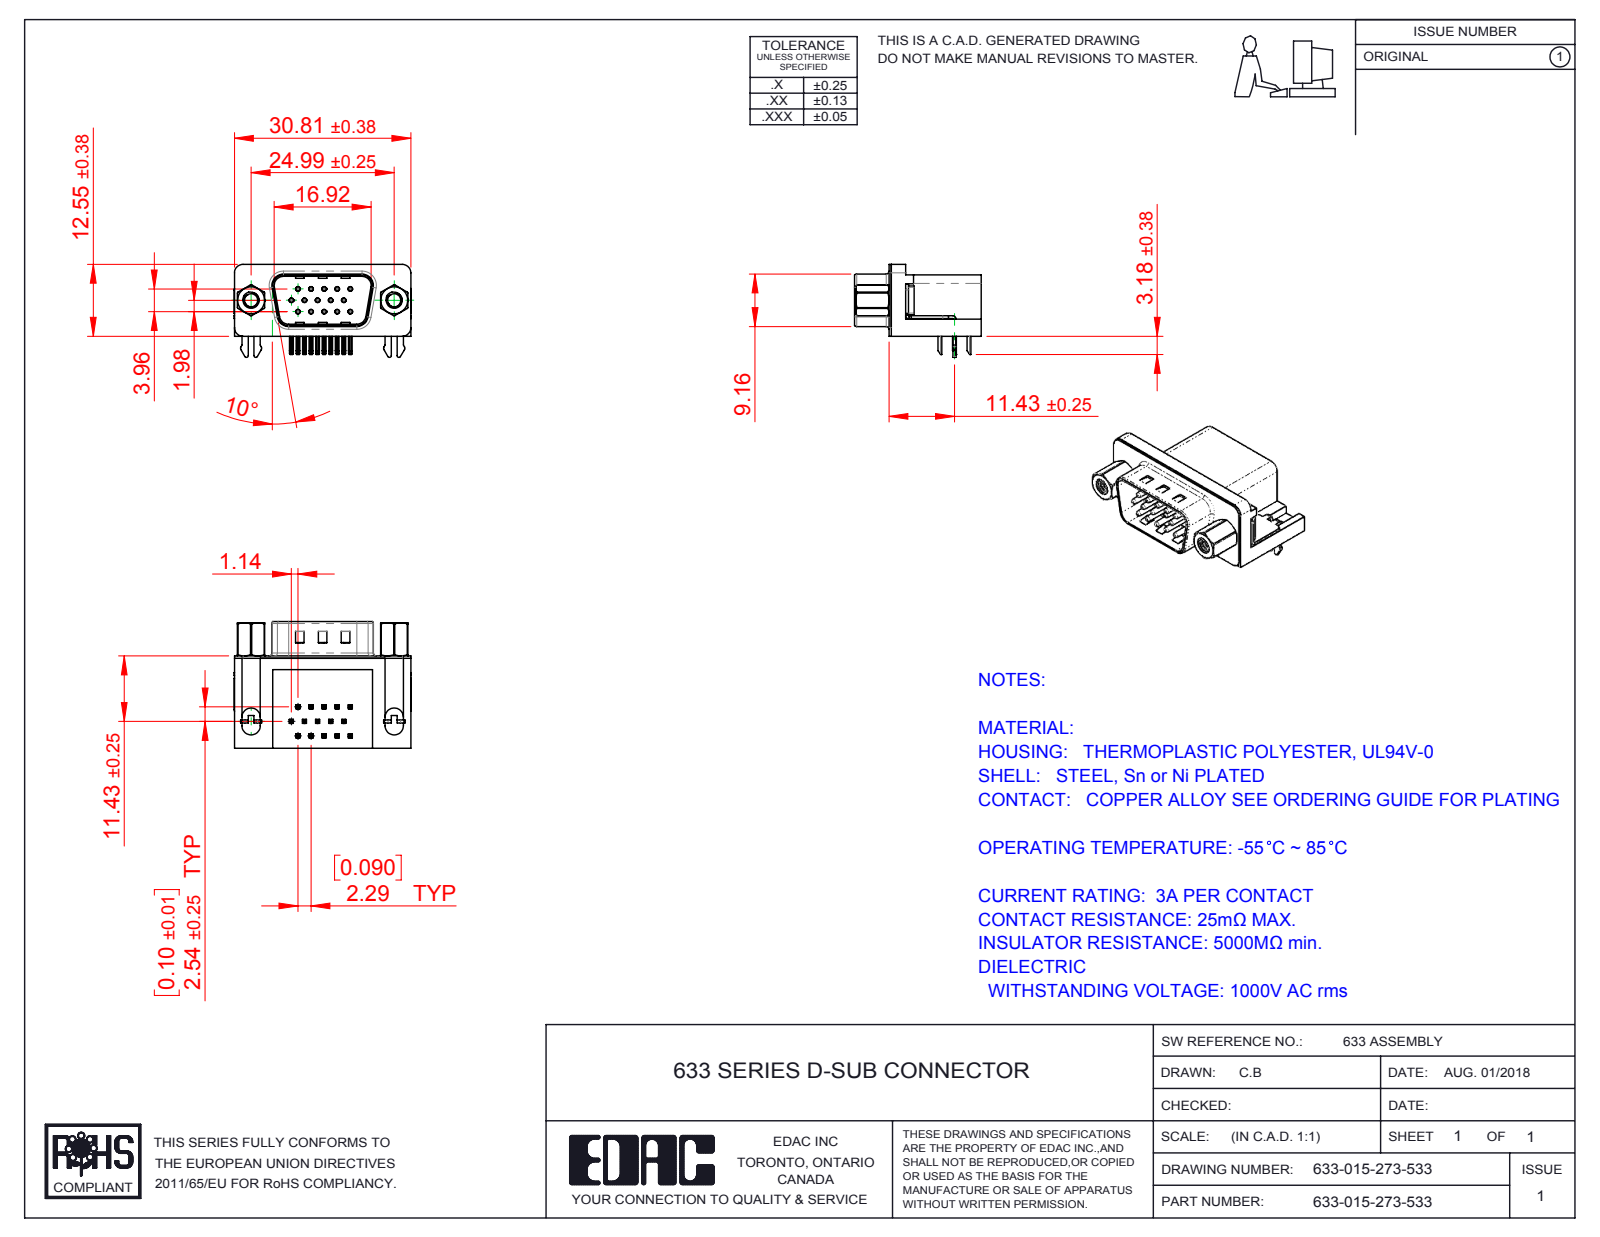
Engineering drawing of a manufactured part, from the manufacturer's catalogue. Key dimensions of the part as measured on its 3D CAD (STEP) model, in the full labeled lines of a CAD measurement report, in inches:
Part name (STEP PRODUCT): 633 4-40 Threaded Rivet; 633-015-273-533; 633 Contact Top; 633 2 Prong Board Lock (+6 more)
STEP written by: SolidWorks 2016 (CONFIG_CONTROL_DESIGN)
Units: inches
Bodies: 23 solids, 1603 faces (915 planar, 515 cylindrical, 173 other)
Overall size (bounding box): 1.216 × 0.87 × 0.64
Volume: 0.261 in³ · Surface area: 9.112 in²
Round holes (diameter × count): ⌀0.014 ×15, ⌀0.031 ×15, ⌀0.089 ×2, ⌀0.09 ×2, ⌀0.157 ×2, ⌀0.189 ×2, ⌀0.197 ×2
Round bosses / shafts (diameter × count): ⌀0.03 ×15, ⌀0.193 ×2, ⌀0.187 ×2, ⌀0.154 ×2, ⌀0.11 ×2
Partial cylindrical surfaces — rounded edges, fillets, slot ends (radius × count): R0.01 ×68, R0.005 ×30, R0.039 ×16, R0.02 ×14, R0.063 ×8, R0.059 ×7, R0.013 ×4, R0.035 ×4
Main face-to-face distances: 0.016, 0.407, 0.618, 0.634, 0.114, 0.02, 0.098, 0.264, 0.014, 0.421
Hole centre spacings: 0.156, 0.09, 0.18, 0.09, 0.238, 0.27, 0.312, 0.238
